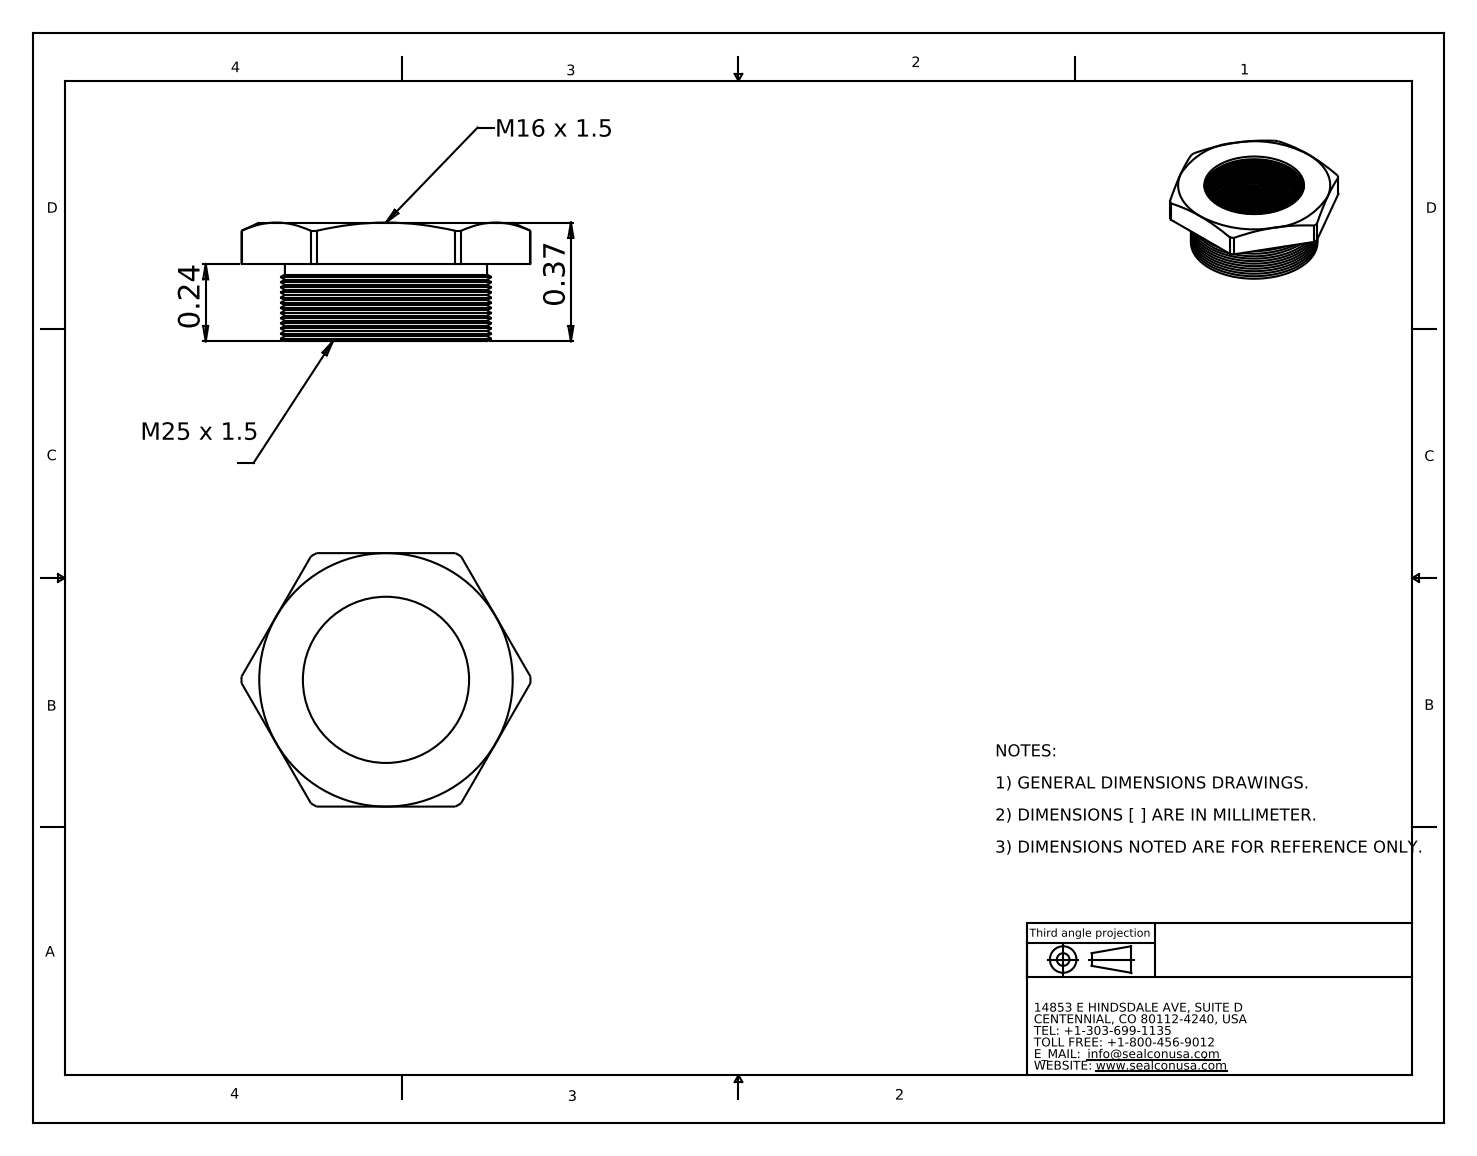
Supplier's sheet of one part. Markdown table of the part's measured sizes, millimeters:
| quantity | value |
| --- | --- |
| part name | RM-2516-SS |
| STEP written by | SolidWorks 2008 (CONFIG_CONTROL_DESIGN) |
| units | millimeters |
| bodies | 1 solid, 241 faces (9 planar, 81 cylindrical, 151 other) |
| overall size | 22.9 × 20.1 × 9.4 |
| volume | 1 100 mm³ |
| surface area | 1 999 mm² |
| round holes (diameter × count) | 13.2 × 1 |
| round bosses / shafts (diameter × count) | 16 × 1 |
| partial cylindrical surfaces (radius × count) | 11.4 × 1 |
| main face-to-face distances | 3.3, 20.1, 6.1, 9.4 |
